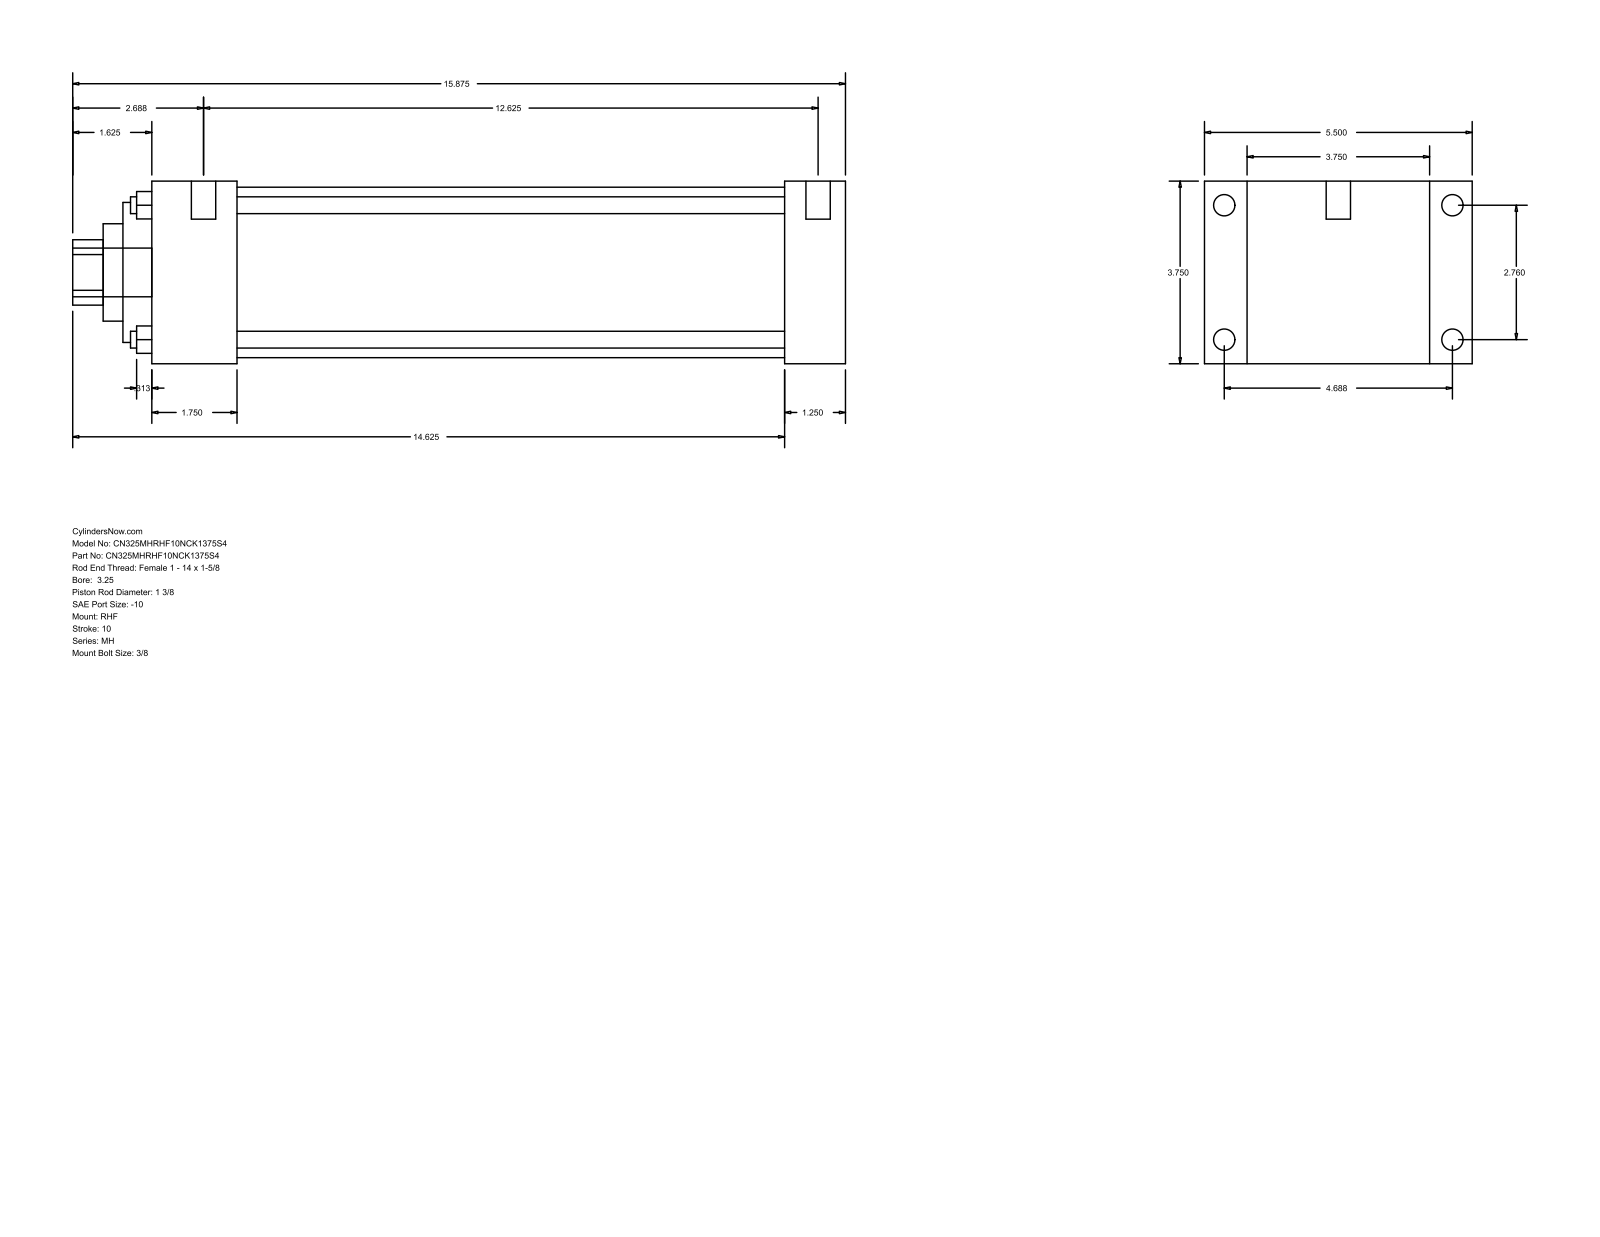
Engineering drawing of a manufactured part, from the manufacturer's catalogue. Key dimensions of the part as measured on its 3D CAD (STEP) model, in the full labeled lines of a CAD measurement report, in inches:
Part name (STEP PRODUCT): MH_RHF__0325_1.375
STEP written by: GSSL Pune (CONFIG_CONTROL_DESIGN)
Units: inches
Bodies: 0 solids, 90 faces (61 planar, 29 cylindrical, 0 other)
Overall size (bounding box): 15.875 × 5.5 × 3.75
Round holes (diameter × count): ⌀0.345 ×4, ⌀1.375 ×1, ⌀2 ×1, ⌀2.875 ×1, ⌀3.5 ×1
Round bosses / shafts (diameter × count): ⌀0.438 ×4, ⌀0.219 ×4, ⌀0.5 ×2, ⌀1 ×1
Partial cylindrical surfaces — rounded edges, fillets, slot ends (radius × count): R0.672 ×1
Main face-to-face distances: 3.75, 1.25, 0.875, 4.625, 13, 14.25, 5.5, 1.75, 11.25, 12.5
Hole centre spacings: 1.952, 2.76, 3.903
